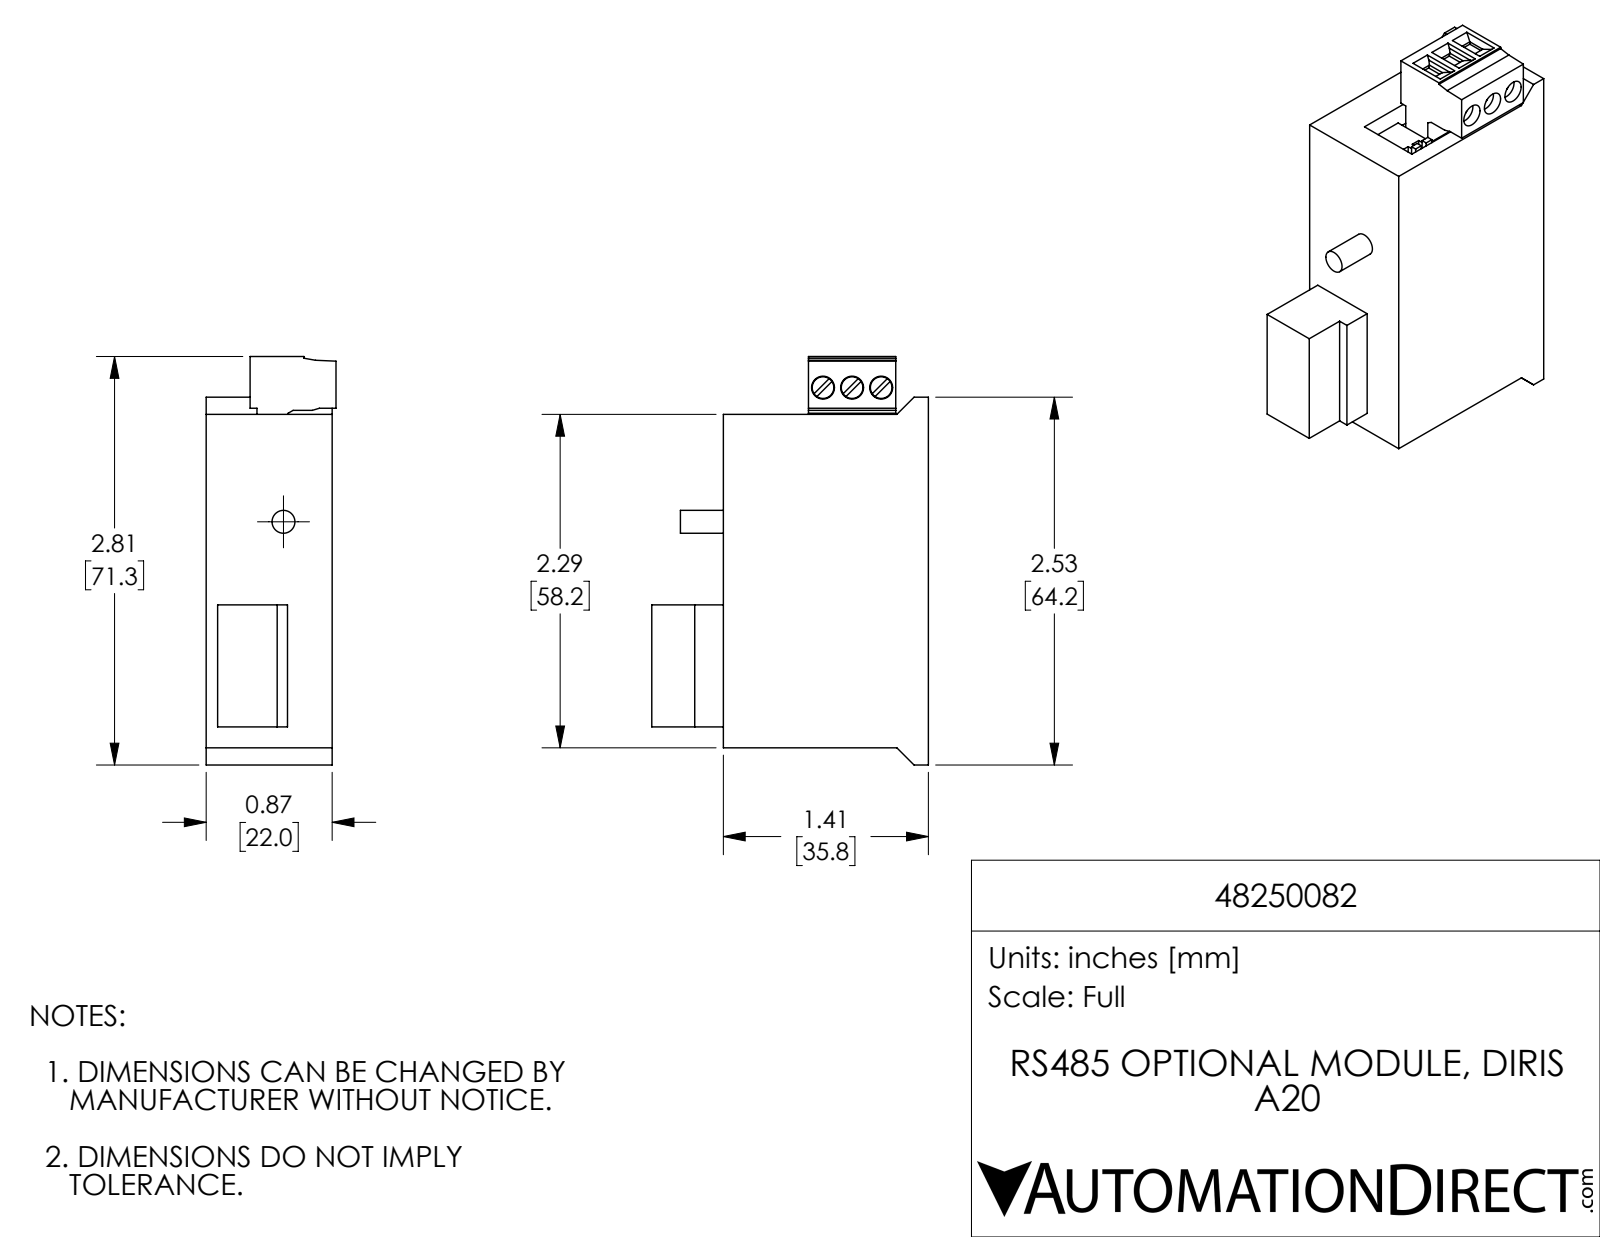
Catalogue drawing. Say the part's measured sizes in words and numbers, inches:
The part is named "48250082". Its 3-D file was written by "SolidWorks 2017 (AUTOMOTIVE_DESIGN)". It is 1 solid with 139 faces: 123 planar, 16 cylindrical and 0 other. Overall it measures 2.807 by 1.902 by 0.893 inches. Its volume is 3.088 cubic inches and its surface area 17.35 square inches. Round holes: 4 of diameter 0.157. Round bosses or shafts: 3 of diameter 0.149. The main face-to-face distances are 0.866, 1.409, 2.291, 0.079, 0.787, 1.902, 0.492, 0.224, 0.824, 0.585. The hole center spacings are 0.2, 0.4.
